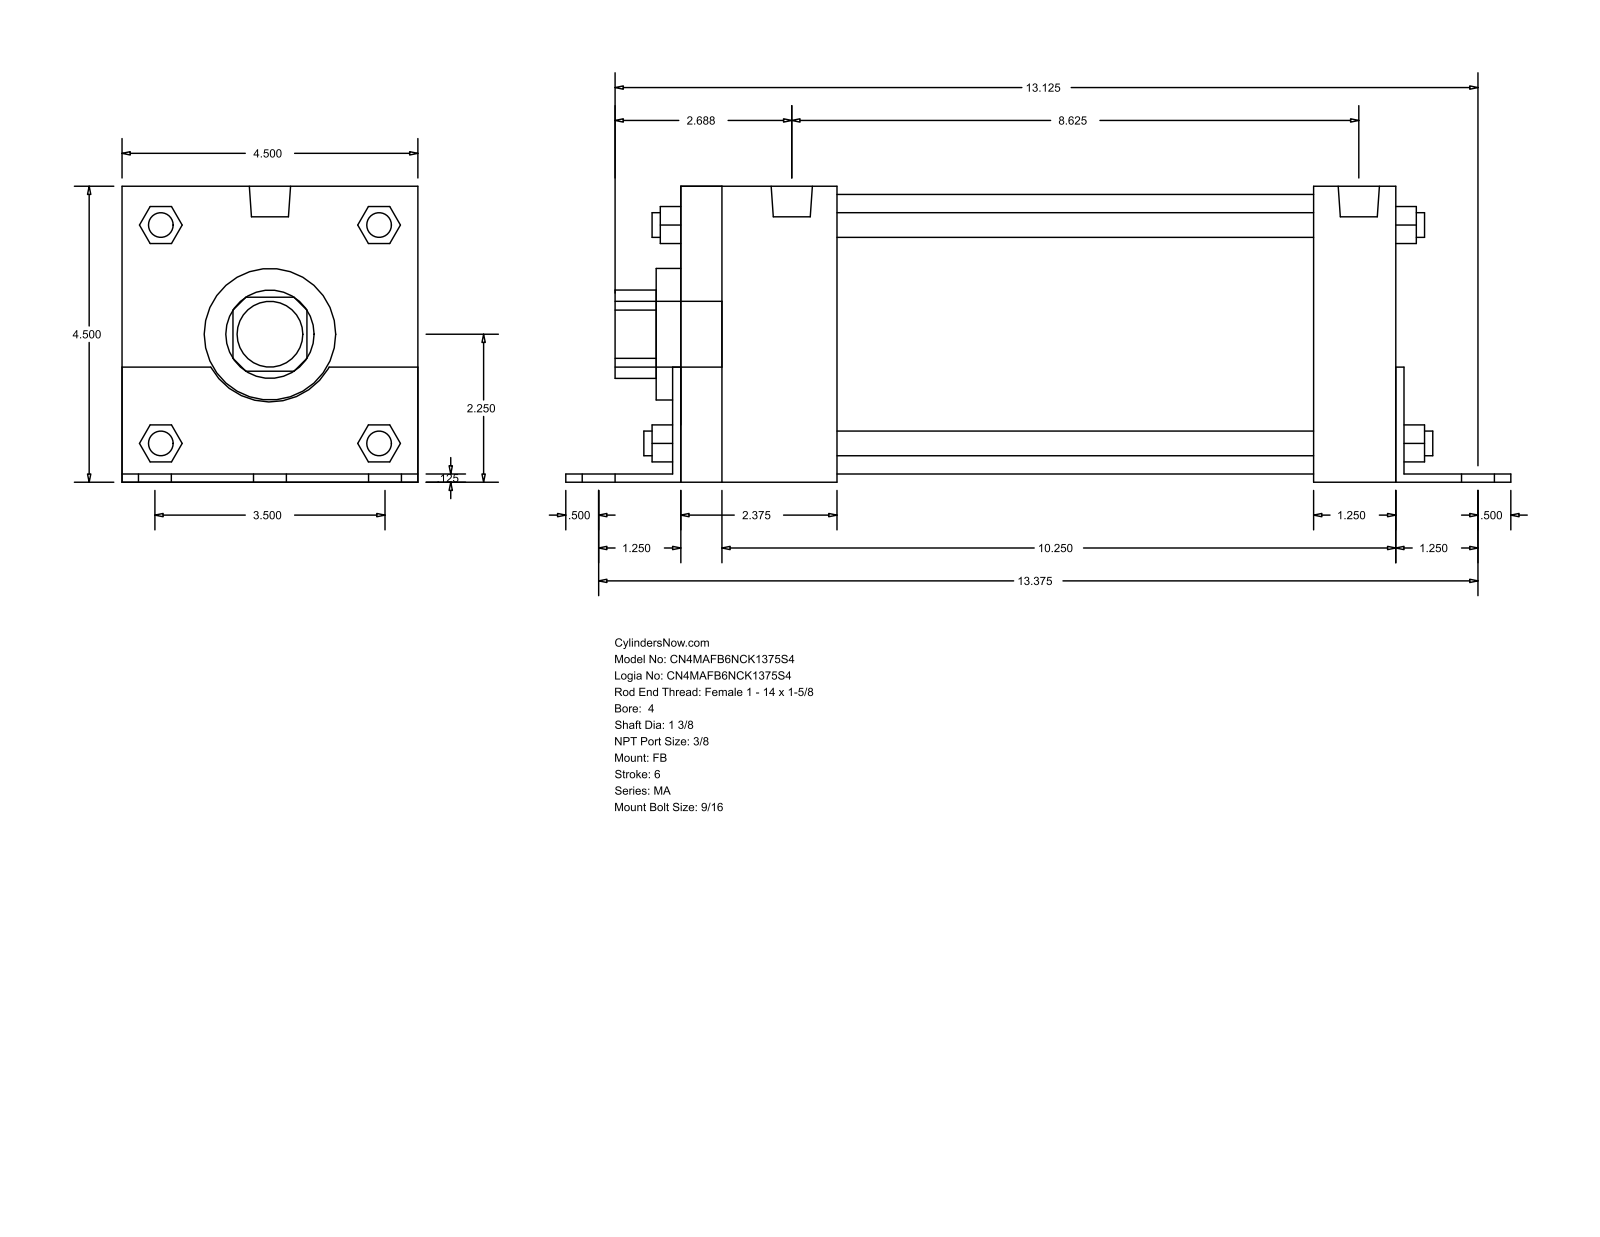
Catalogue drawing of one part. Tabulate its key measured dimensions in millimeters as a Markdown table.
| quantity | value |
| --- | --- |
| part name | MA_FB__0400_1.375 |
| STEP written by | GSSL Pune (CONFIG_CONTROL_DESIGN) |
| units | millimeters |
| bodies | 0 solids, 140 faces (105 planar, 35 cylindrical, 0 other) |
| overall size | 365.12 × 114.35 × 114.3 |
| round holes (diameter × count) | 34.92 × 1, 50.8 × 1, 107.95 × 1 |
| round bosses / shafts (diameter × count) | 14.29 × 6, 11.11 × 4, 9.53 × 4, 15.93 × 2, 25.4 × 1 |
| partial cylindrical surfaces (radius × count) | 17.06 × 1, 26.16 × 1 |
| main face-to-face distances | 114.3, 3.17, 114.35, 3.12, 111.18, 276.22, 3.18, 279.4, 60.32, 279.39 |
